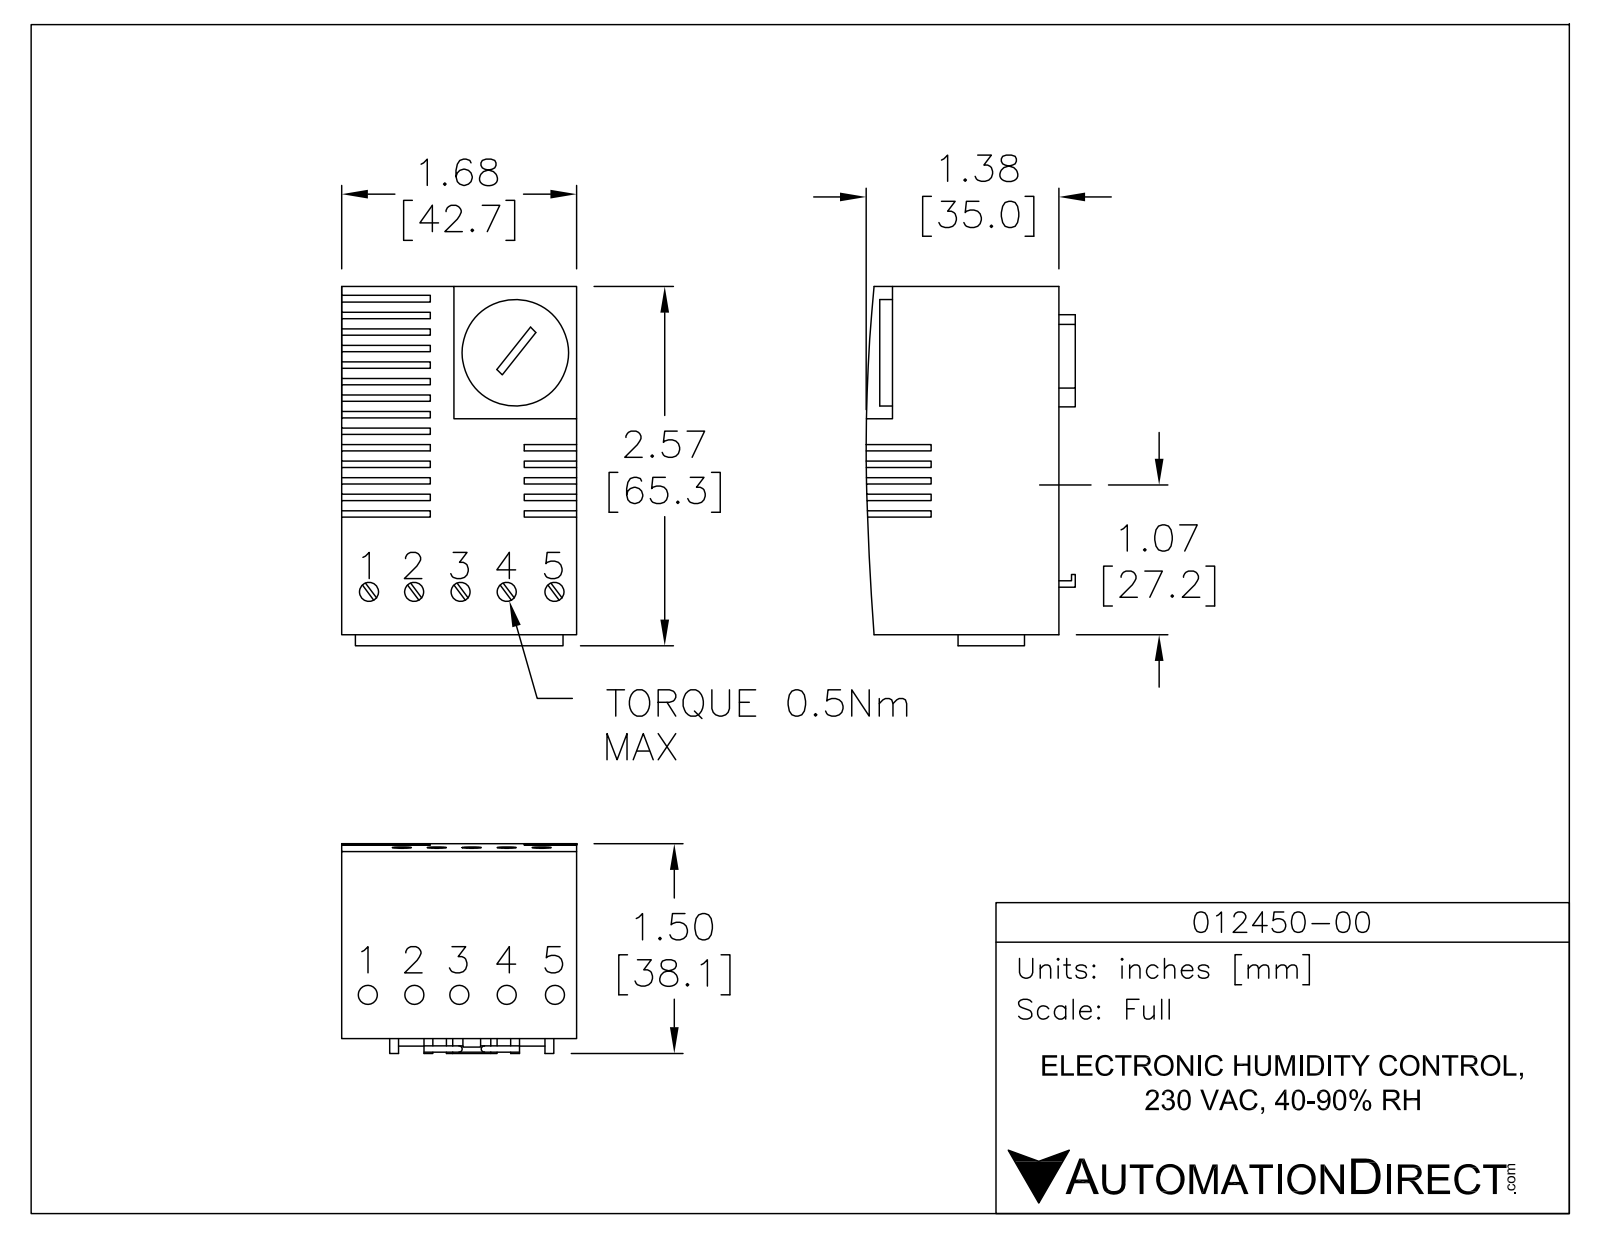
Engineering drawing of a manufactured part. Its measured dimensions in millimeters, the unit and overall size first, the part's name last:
Units: millimetres
Overall size (bounding box): 65.4 × 42.8 × 38.1
Round holes (diameter × count): ⌀3.8 ×10, ⌀15 ×1
Partial cylindrical surfaces — rounded edges, fillets, slot ends (radius × count): R0.7 ×66, R1.5 ×11, R0.8 ×10, R0.7 ×5, R0.5 ×1, R3.8 ×1, R318.7 ×1, R328.7 ×1
Main face-to-face distances: 3, 42.8, 6.1, 63.5, 1.4, 19.9, 30.5, 1.7, 4.7, 6.1
Hole centre spacings: 7.6, 15.2, 22.9, 30.5, 42.6, 43.1, 43.4, 45.5
Volume: 82 260 mm³ · Surface area: 18 880 mm²
Bodies: 1 solid, 392 faces (154 planar, 138 cylindrical, 100 other)
Part name (STEP PRODUCT): 012450-00
STEP written by: SolidWorks 2013 (AUTOMOTIVE_DESIGN)
